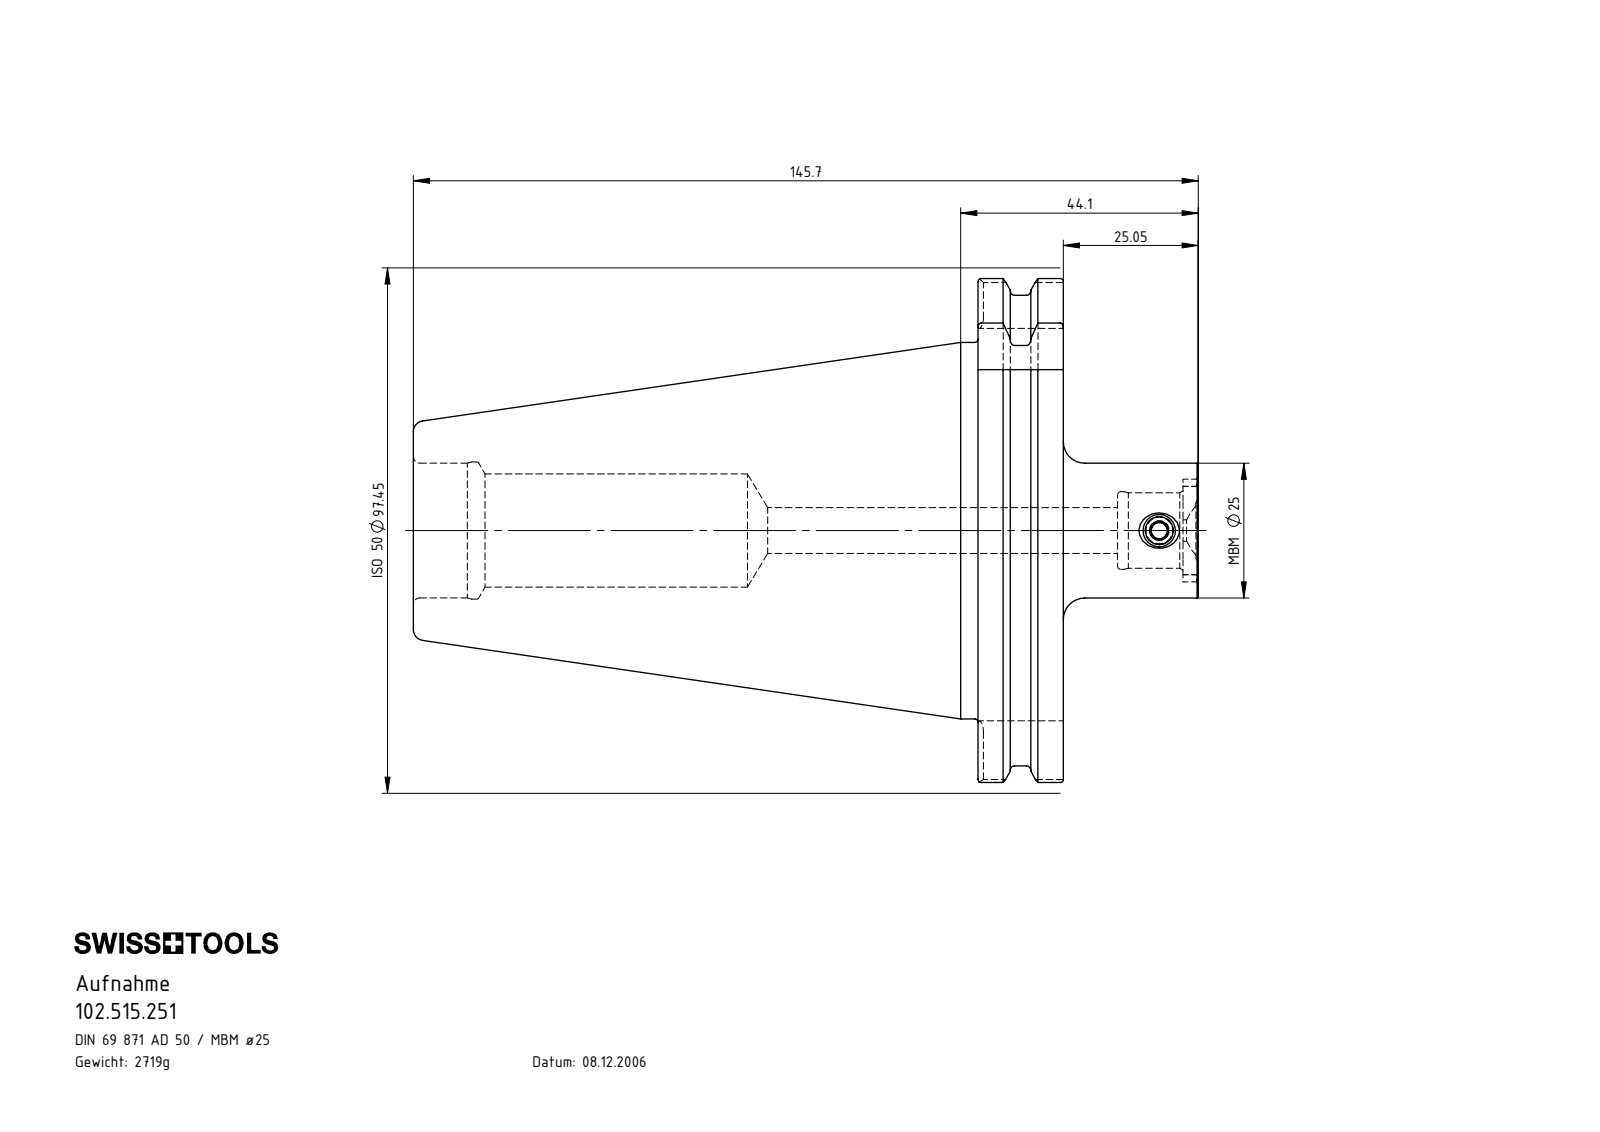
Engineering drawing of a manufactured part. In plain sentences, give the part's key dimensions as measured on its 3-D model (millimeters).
The part is named "SK5-MB2.K01.044_C; MB2-ER1.001.008_A; 102.515.251". Its 3-D file was written by "SolidWorks 2017 (CONFIG_CONTROL_DESIGN)". It is 2 solids with 169 faces: 53 planar, 50 cylindrical and 66 other. Overall it measures 145.7 by 97.45 by 93.51 millimeters. Its volume is 346 351 cubic millimeters and its surface area 44 064 square millimeters. Round holes: 1 of diameter 3, 1 of diameter 5.25, 1 of diameter 8.5, 1 of diameter 14, 1 of diameter 14.4, 1 of diameter 21, 1 of diameter 25, 1 of diameter 25.45. Round bosses or shafts: 1 of diameter 91, 1 of diameter 69.85, 1 of diameter 6. Partial cylindrical surfaces (rounded edges, fillets, slot ends): 8 of radius 2, 4 of radius 2.7, 1 of radius 8, 1 of radius 9.53, 1 of radius 48.73. The main face-to-face distances are 15.85, 104.8, 120.65, 72.8, 25.7, 145.7, 40.9, 25.05, 42.7, 17.
